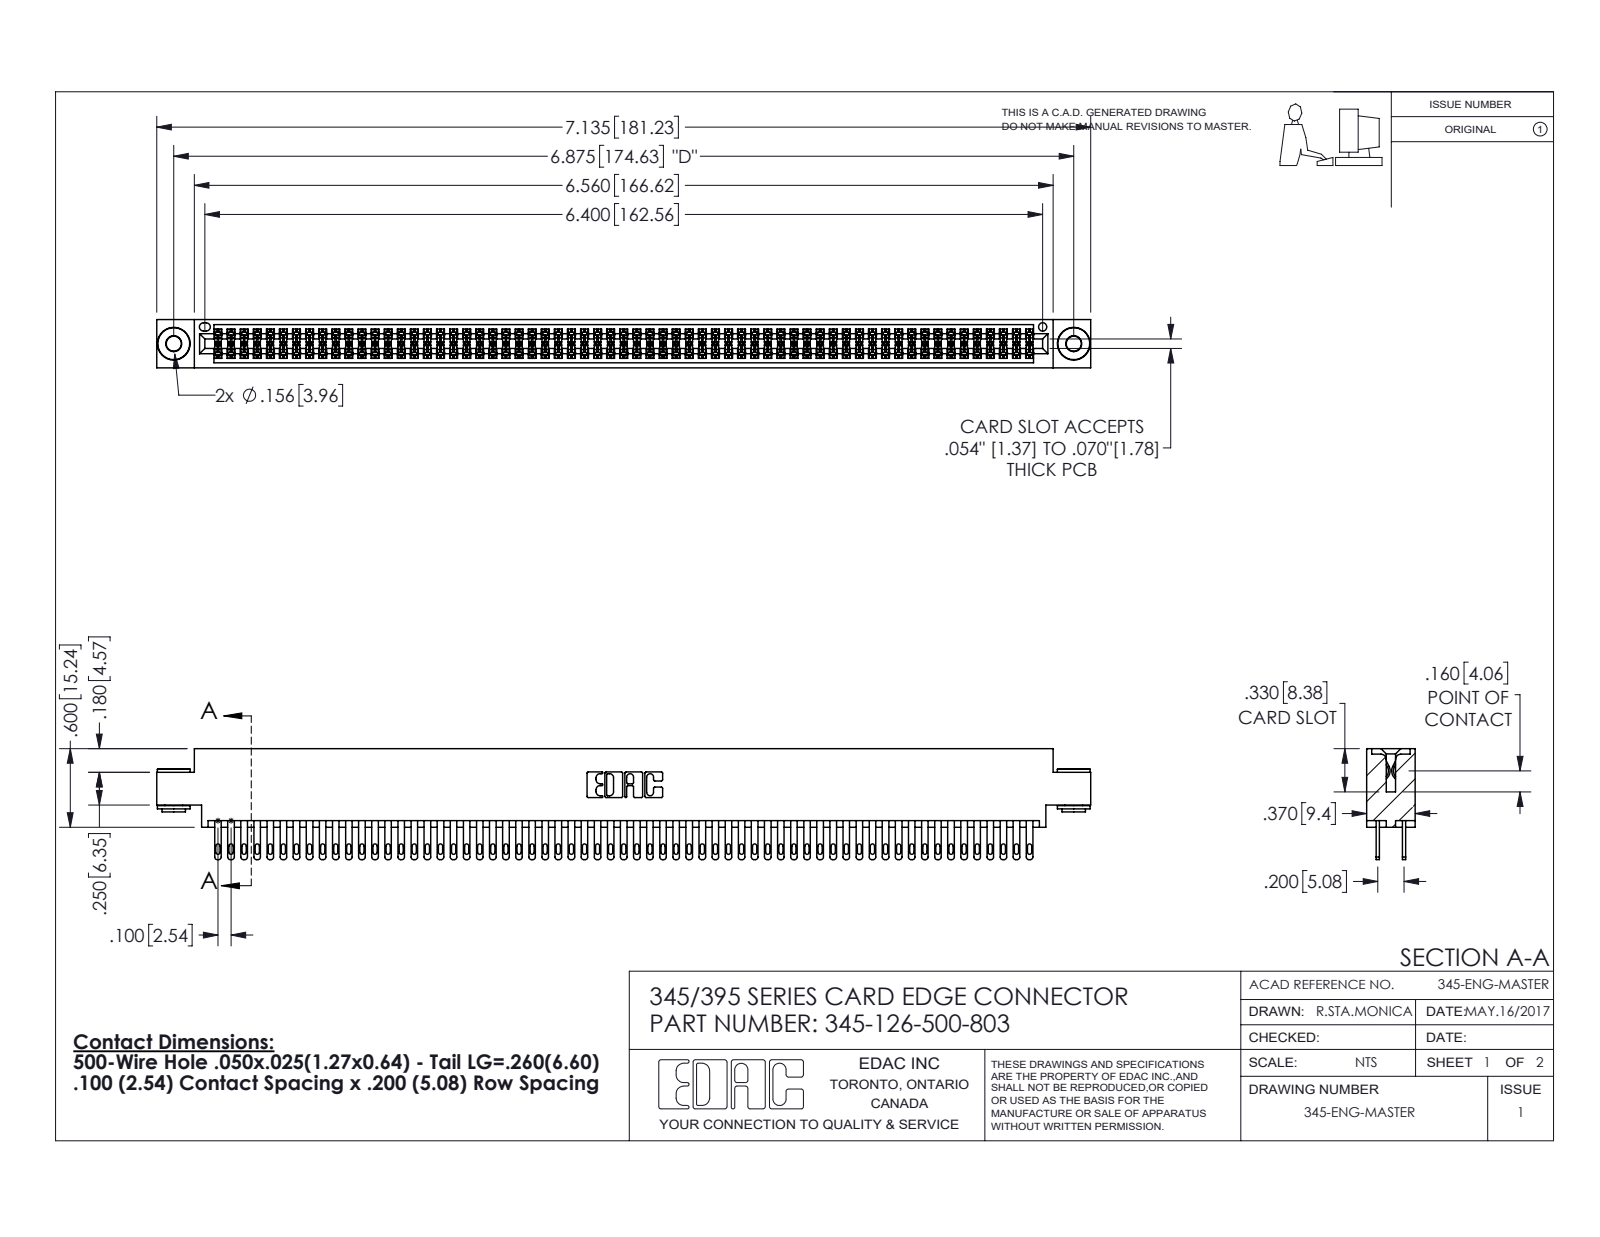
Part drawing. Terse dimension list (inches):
name: 345-250-002_345-250-002-102; 345-292-001_345-293-100; 345 Part_0.170 Offset - 0.156 Dia-TH; 345-126-500-803
written by: SolidWorks 2016 (CONFIG_CONTROL_DESIGN)
unit: in
bodies: 129 solids, 5964 faces (3496 planar, 2460 cylindrical, 8 other)
size: 7.135 × 0.847 × 0.37
volume: 1.104 in³; area: 44.61 in²
holes: 2× ⌀0.116, 2× ⌀0.156, 1× ⌀0.064
bosses: 2× ⌀0.25, 2× ⌀0.18, 2× ⌀0.136
rounds: 189× R0.006, 126× R0.016, 126× R0.02, 22× R0.01, 6× R0.007, 6× R0.031, 3× R0.026, 2× R0.014
face distances: 0.072, 0.298, 0.2, 0.098, 0.272, 0.025, 0.37, 0.225, 0.175, 0.149
hole spacings: 0.27, 6.639, 6.875
